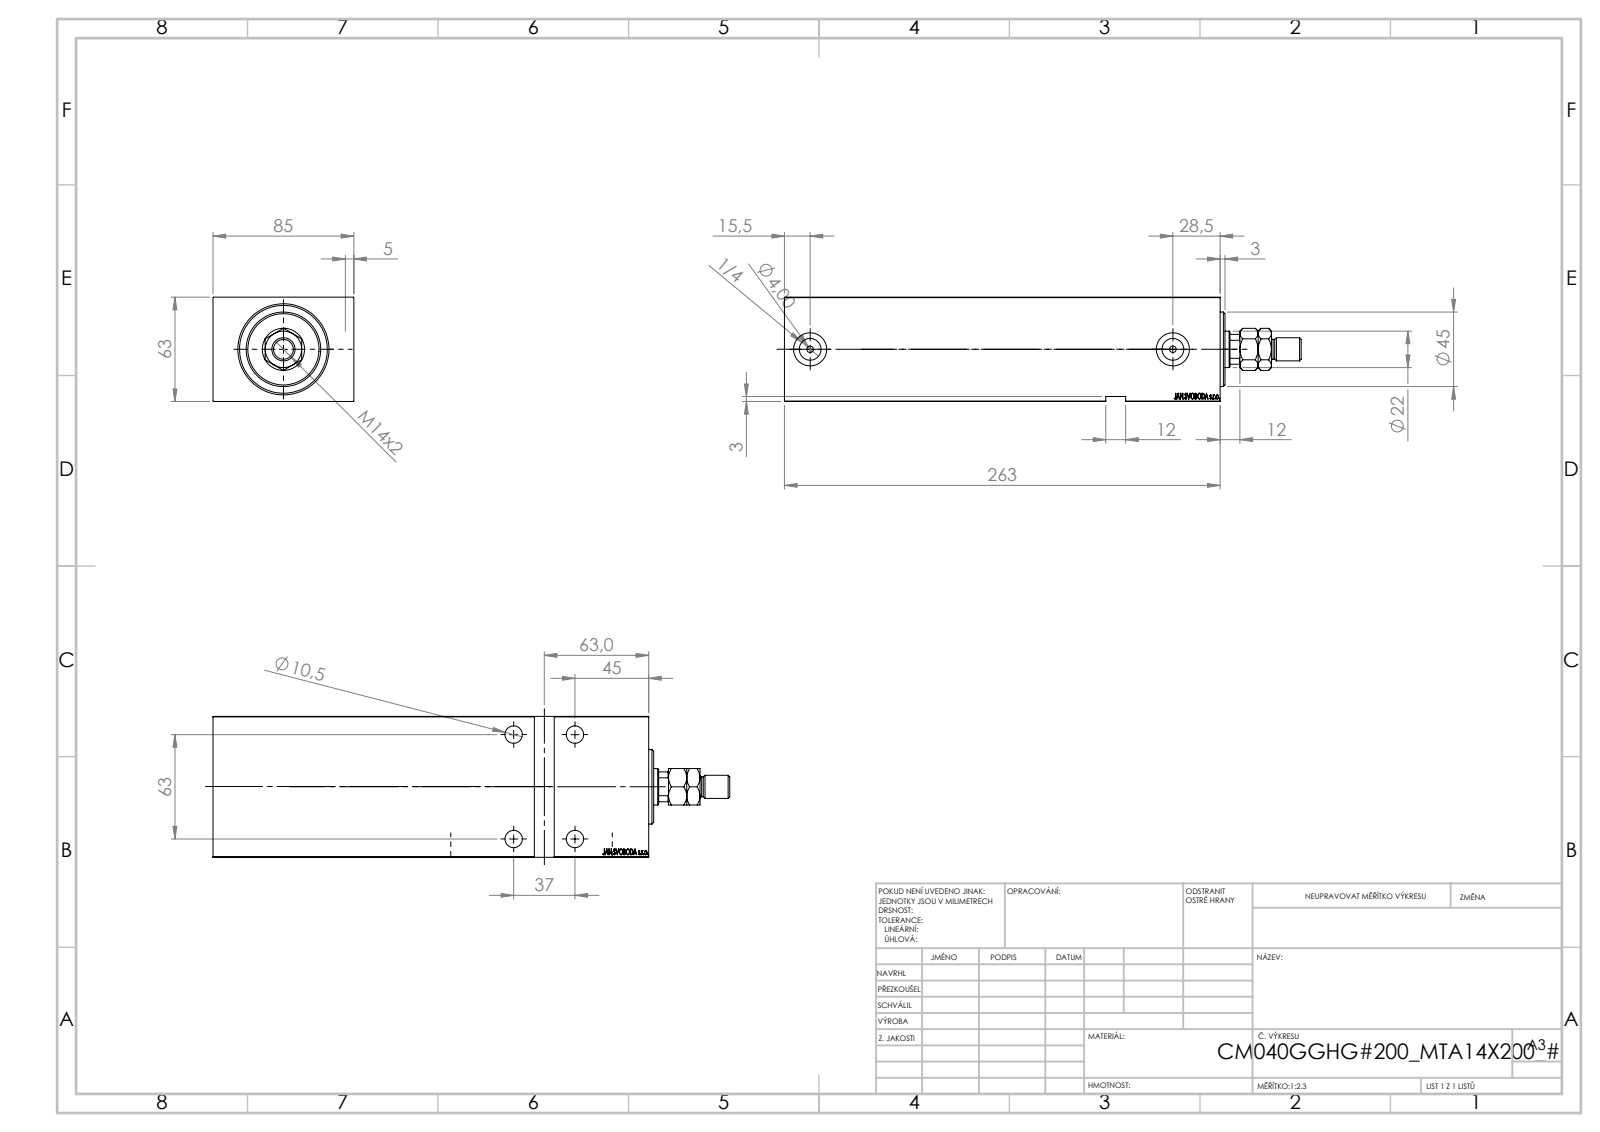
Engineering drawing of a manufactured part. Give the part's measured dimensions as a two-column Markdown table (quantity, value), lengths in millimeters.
| quantity | value |
| --- | --- |
| part name | V450CM_G_VCP; MTA; V450CM_VC_G; Zatka_OIL_PORT (+1 more) |
| STEP written by | SolidWorks 2019 (CONFIG_CONTROL_DESIGN) |
| units | millimeters |
| bodies | 6 solids, 946 faces (456 planar, 62 cylindrical, 428 other) |
| overall size | 312 × 85 × 63 |
| volume | 1 208 000 mm³ |
| surface area | 165 603 mm² |
| round holes (diameter × count) | 10.5 × 4, 16.5 × 4, 4 × 2, 13.16 × 2, 20 × 2, 12.5 × 1, 22 × 1, 25.5 × 1, 40 × 1, 42 × 1, 53 × 1 |
| round bosses / shafts (diameter × count) | 18 × 2, 45 × 1, 27 × 1, 14 × 1, 12 × 1 |
| partial cylindrical surfaces (radius × count) | 10.5 × 1 |
| main face-to-face distances | 63, 85, 263, 12, 251, 5, 258, 246, 3, 60 |
| hole center spacings | 37, 63, 73.06, 219 |
